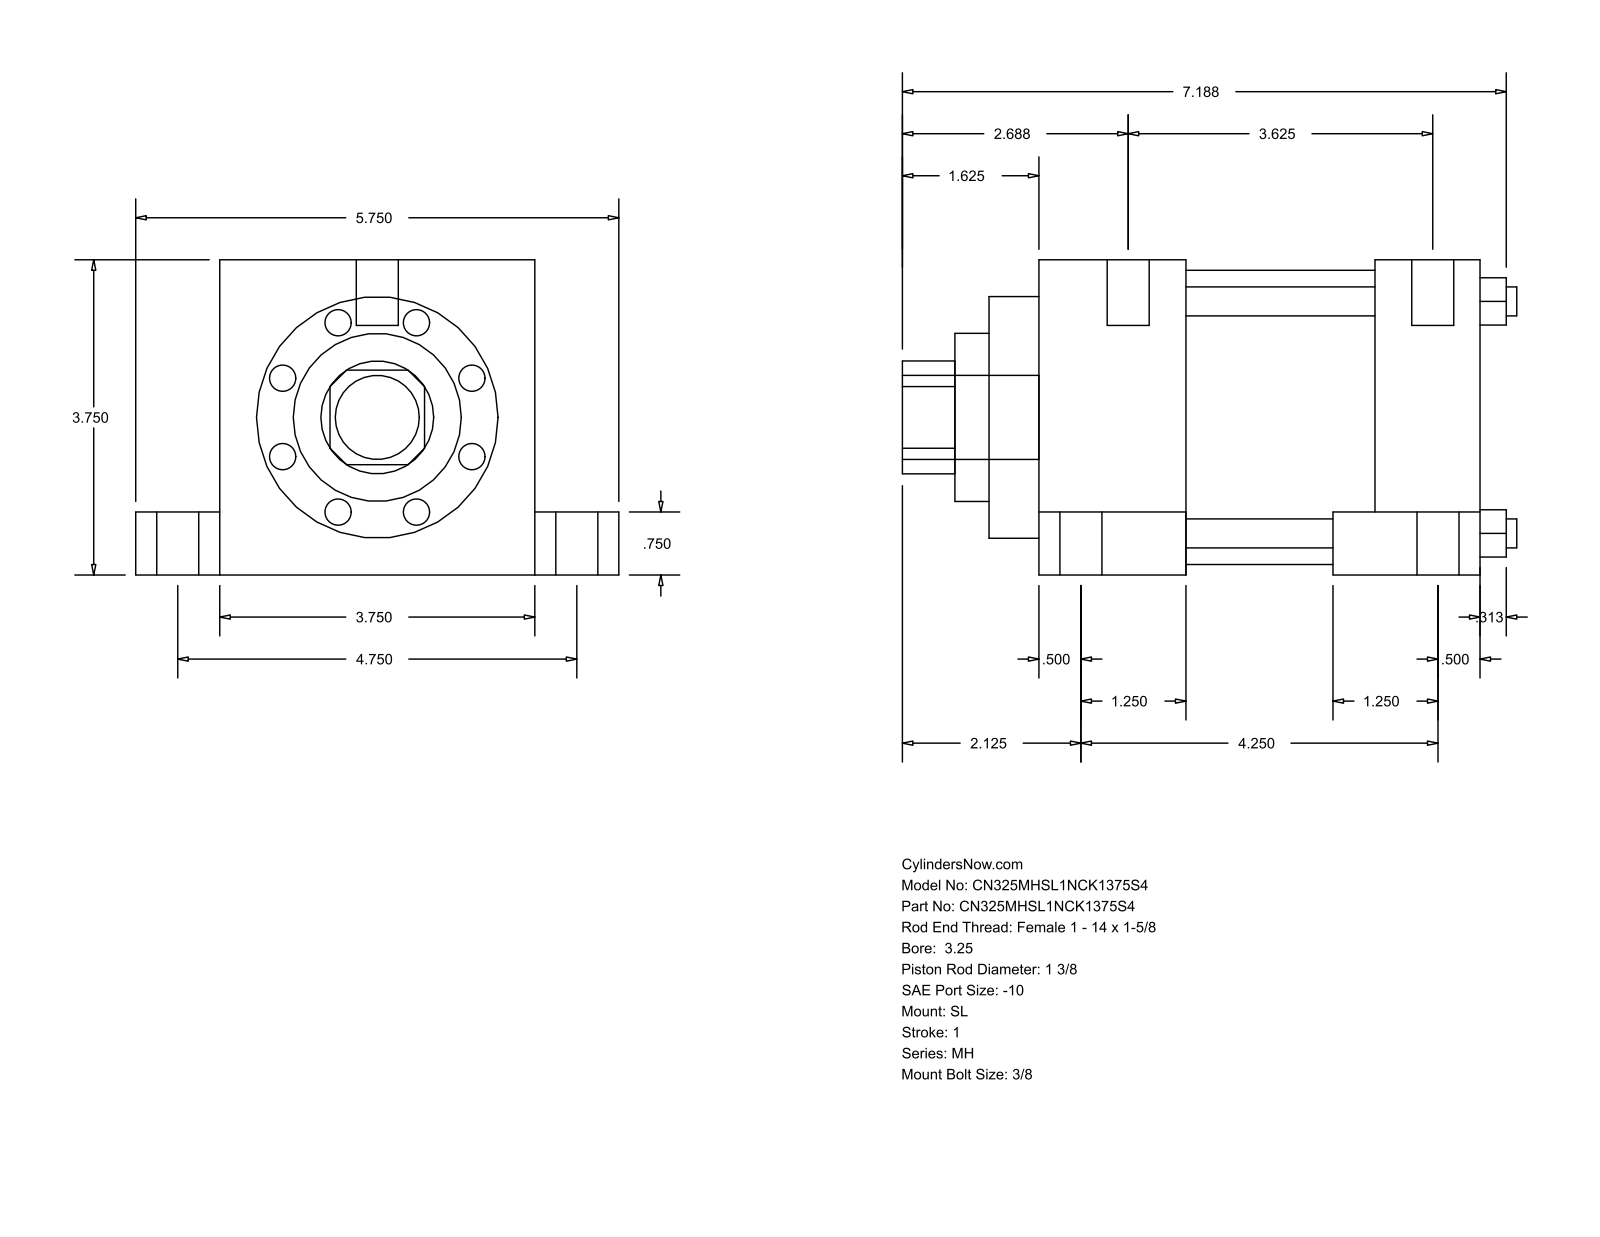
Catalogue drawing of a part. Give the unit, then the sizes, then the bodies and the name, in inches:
Units: inches
Overall size (bounding box): 7.313 × 5.75 × 3.75
Round holes (diameter × count): ⌀0.345 ×4, ⌀1.375 ×1, ⌀2 ×1, ⌀2.875 ×1, ⌀3.5 ×1
Round bosses / shafts (diameter × count): ⌀0.5 ×6, ⌀0.75 ×4, ⌀0.219 ×4, ⌀1 ×1
Partial cylindrical surfaces — rounded edges, fillets, slot ends (radius × count): R0.672 ×1
Main face-to-face distances: 3.75, 5.25, 1.75, 3.5, 1, 4.75, 0.75, 3, 4, 2.25
Hole centre spacings: 1.952, 2.76, 3.903
Bodies: 0 solids, 110 faces (77 planar, 33 cylindrical, 0 other)
Part name (STEP PRODUCT): MH_SL__0325_1.375
STEP written by: GSSL Pune (CONFIG_CONTROL_DESIGN)
